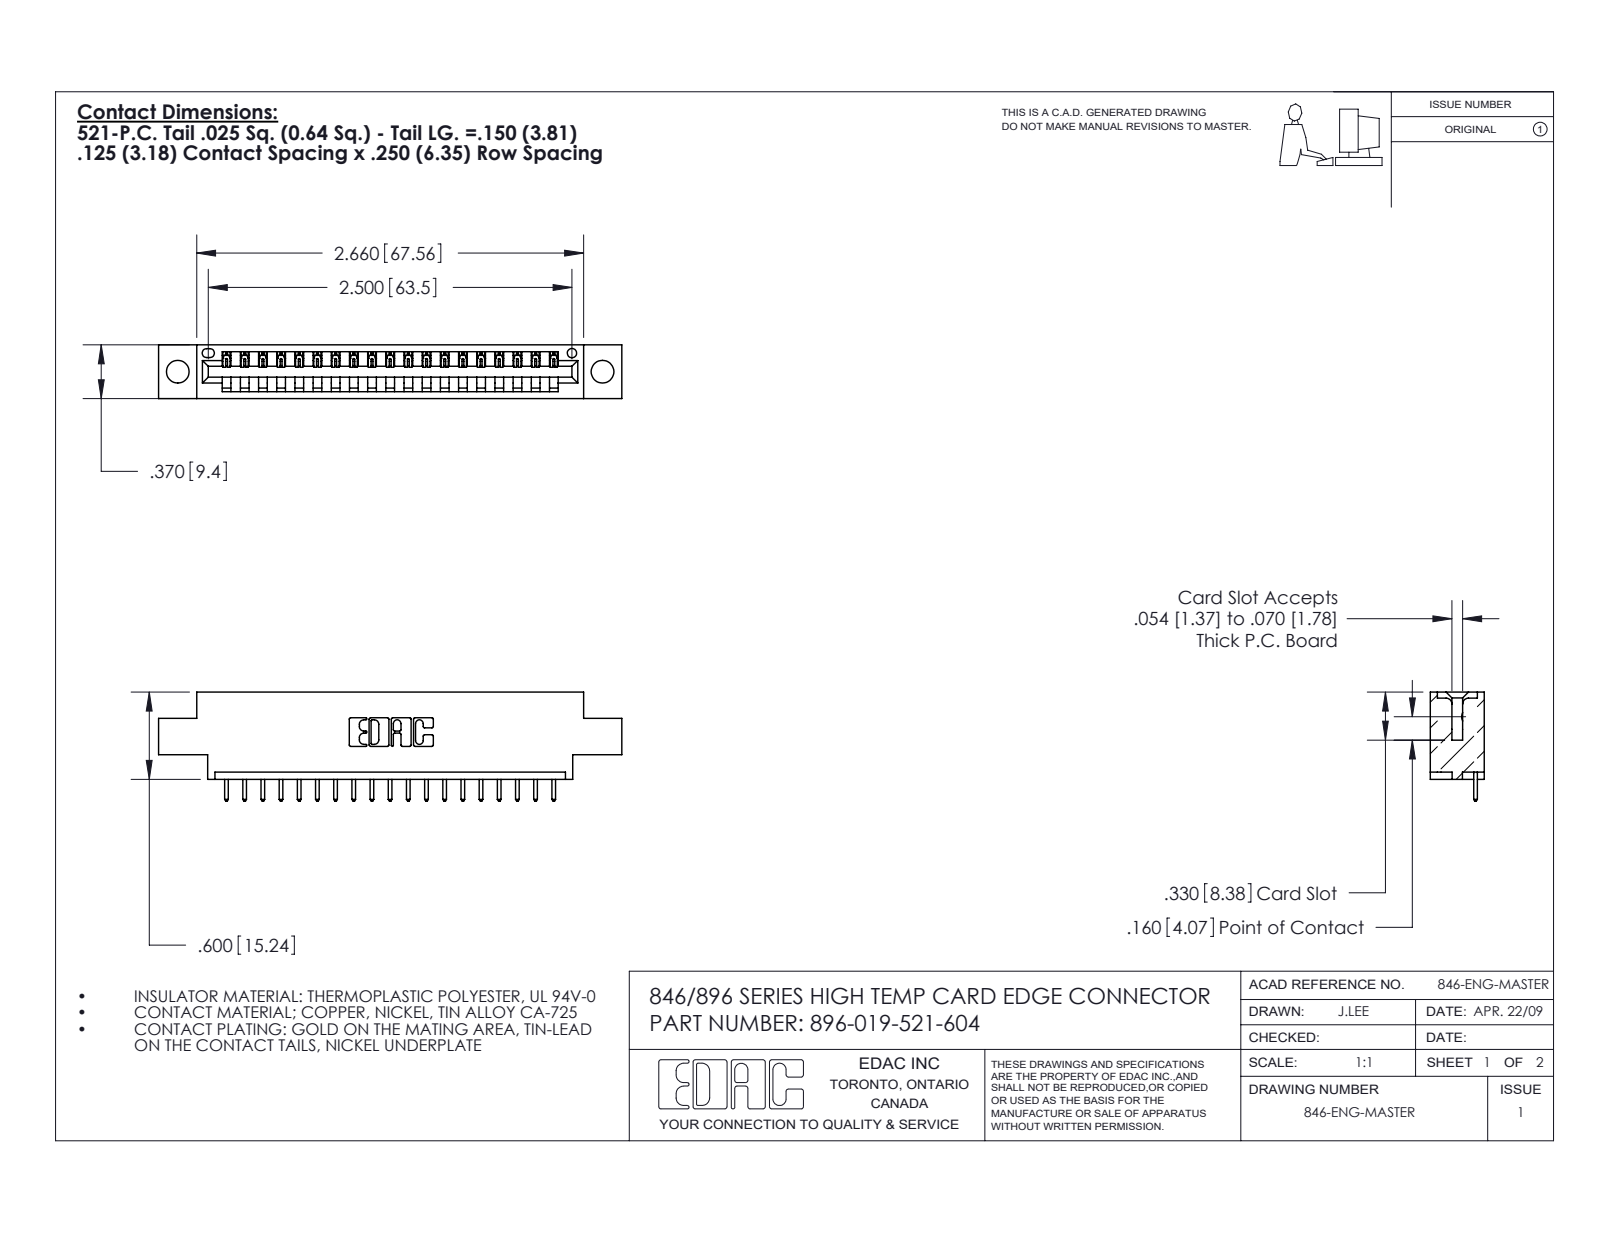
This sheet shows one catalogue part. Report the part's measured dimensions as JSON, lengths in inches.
{"part_name": "346 Part_0.170 Offset - 0.156 Dia-TH; 345-292-001_345-293-121; 396-019-521-604", "step_written_by": "SolidWorks 2016 (CONFIG_CONTROL_DESIGN)", "units": "inches", "bodies": {"solids": 20, "faces": 1228, "planar": 840, "cylindrical": 388, "other": 0}, "overall_size": [3.185, 0.75, 0.37], "volume_in3": 0.445, "surface_area_in2": 13.35, "round_holes": [[0.156, 2], [0.064, 1]], "partial_cylinders_radius": [[0.006, 38], [0.01, 38], [0.01, 22], [0.007, 6], [0.031, 6], [0.026, 3], [0.031, 2], [0.04, 2]], "face_to_face_distances": [0.048, 0.322, 0.37, 0.25, 0.072, 0.298, 0.025, 0.148, 0.222, 0.1], "hole_center_spacings": [0.246, 2.713, 2.92]}
